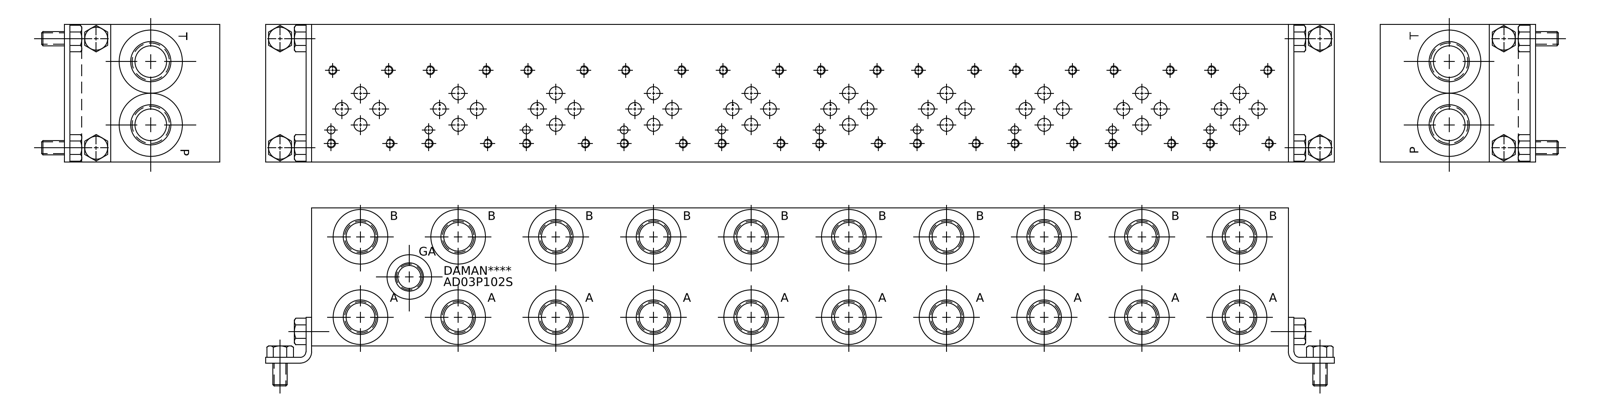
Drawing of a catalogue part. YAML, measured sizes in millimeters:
part_name: "Part_DD03P102S_3D"
step_written_by: "Autodesk Inventor 2019 (AUTOMOTIVE_DESIGN)"
units: millimeters
bodies: {solids: 1, faces: 1355, planar: 627, cylindrical: 266, other: 462}
overall_size: [539.75, 76.2, 76.2]
volume: 2938000
surface_area: 227789
round_holes:
  - {diameter: 3.78, count: 40}
  - {diameter: 4.83, count: 40}
  - {diameter: 7.14, count: 30}
  - {diameter: 14.3, count: 20}
  - {diameter: 17.5, count: 20}
  - {diameter: 19.05, count: 20}
  - {diameter: 19.25, count: 20}
  - {diameter: 30.63, count: 20}
  - {diameter: 3.96, count: 10}
  - {diameter: 6.35, count: 10}
  - {diameter: 6.53, count: 2}
  - {diameter: 7.92, count: 2}
face_to_face_distances: [76.2, 0.79, 75.41, 539.75, 538.96, 538.17, 14.27, 15.06, 61.14, 1]
hole_center_spacings: [107.95, 215.9, 53.98, 323.85, 53.97, 161.93, 118.61, 161.92]
